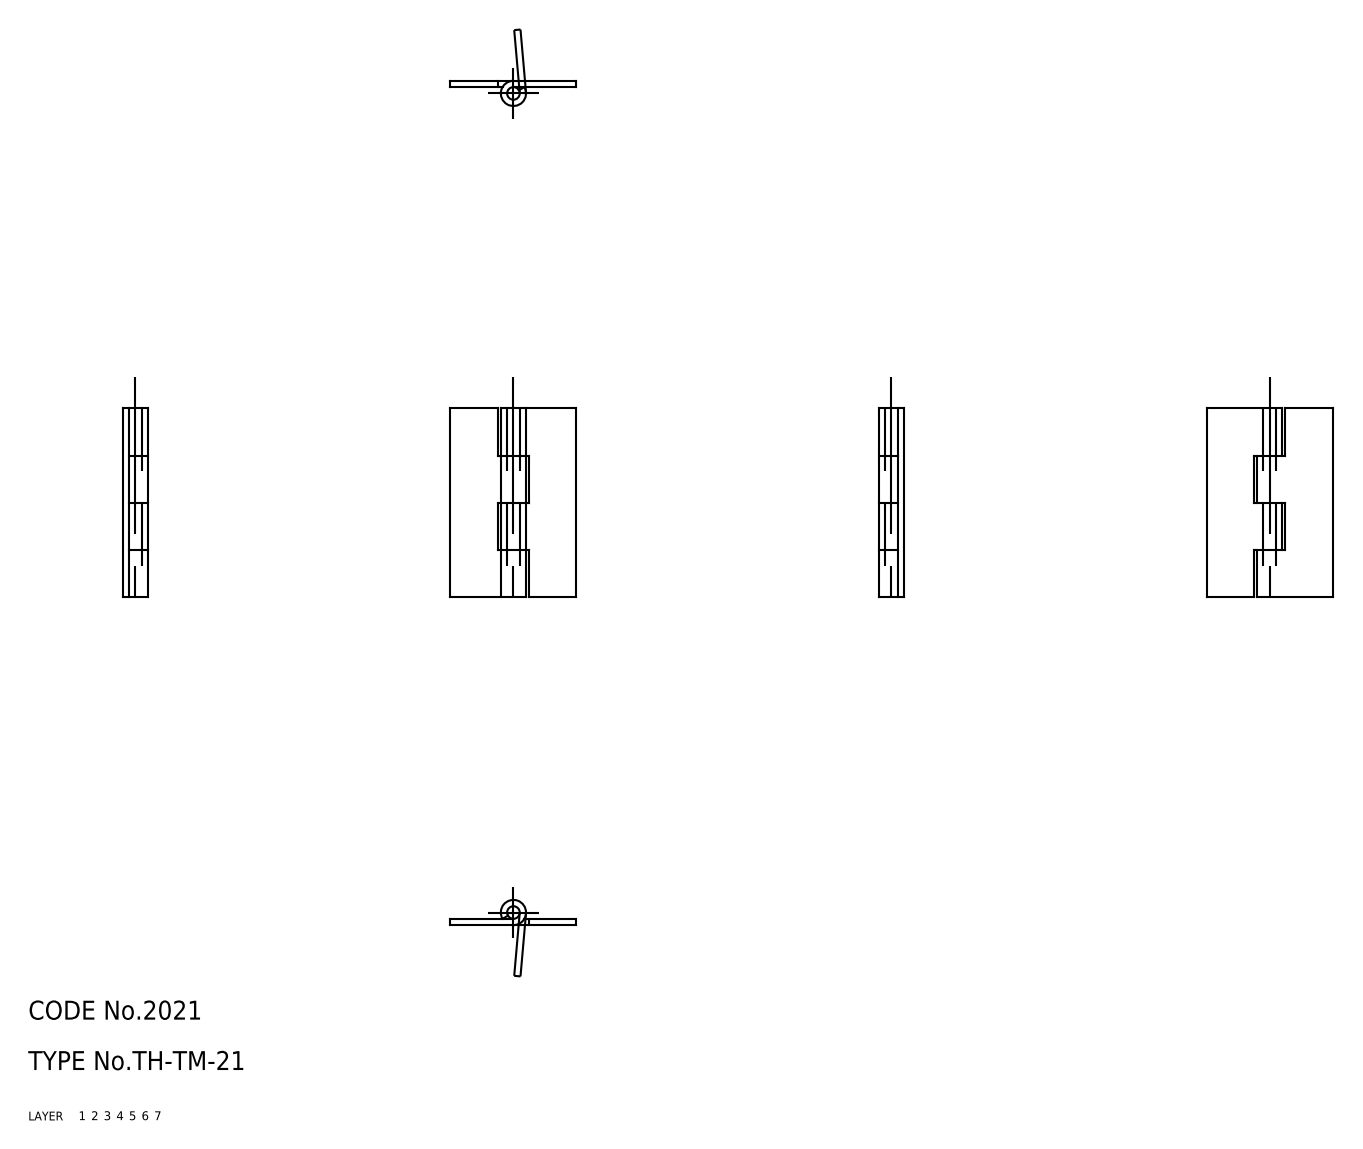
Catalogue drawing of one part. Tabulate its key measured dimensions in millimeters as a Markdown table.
| quantity | value |
| --- | --- |
| part name | hinge piece_B; hinge piece_A; shaft; TH_TM_21_21997_36 |
| STEP written by | CADfix (AUTOMOTIVE_DESIGN) |
| units | millimeters |
| bodies | 3 solids, 36 faces (0 planar, 0 cylindrical, 36 other) |
| overall size | 30 × 20 × 4 |
| volume | 854 mm³ |
| surface area | 1 946 mm² |
